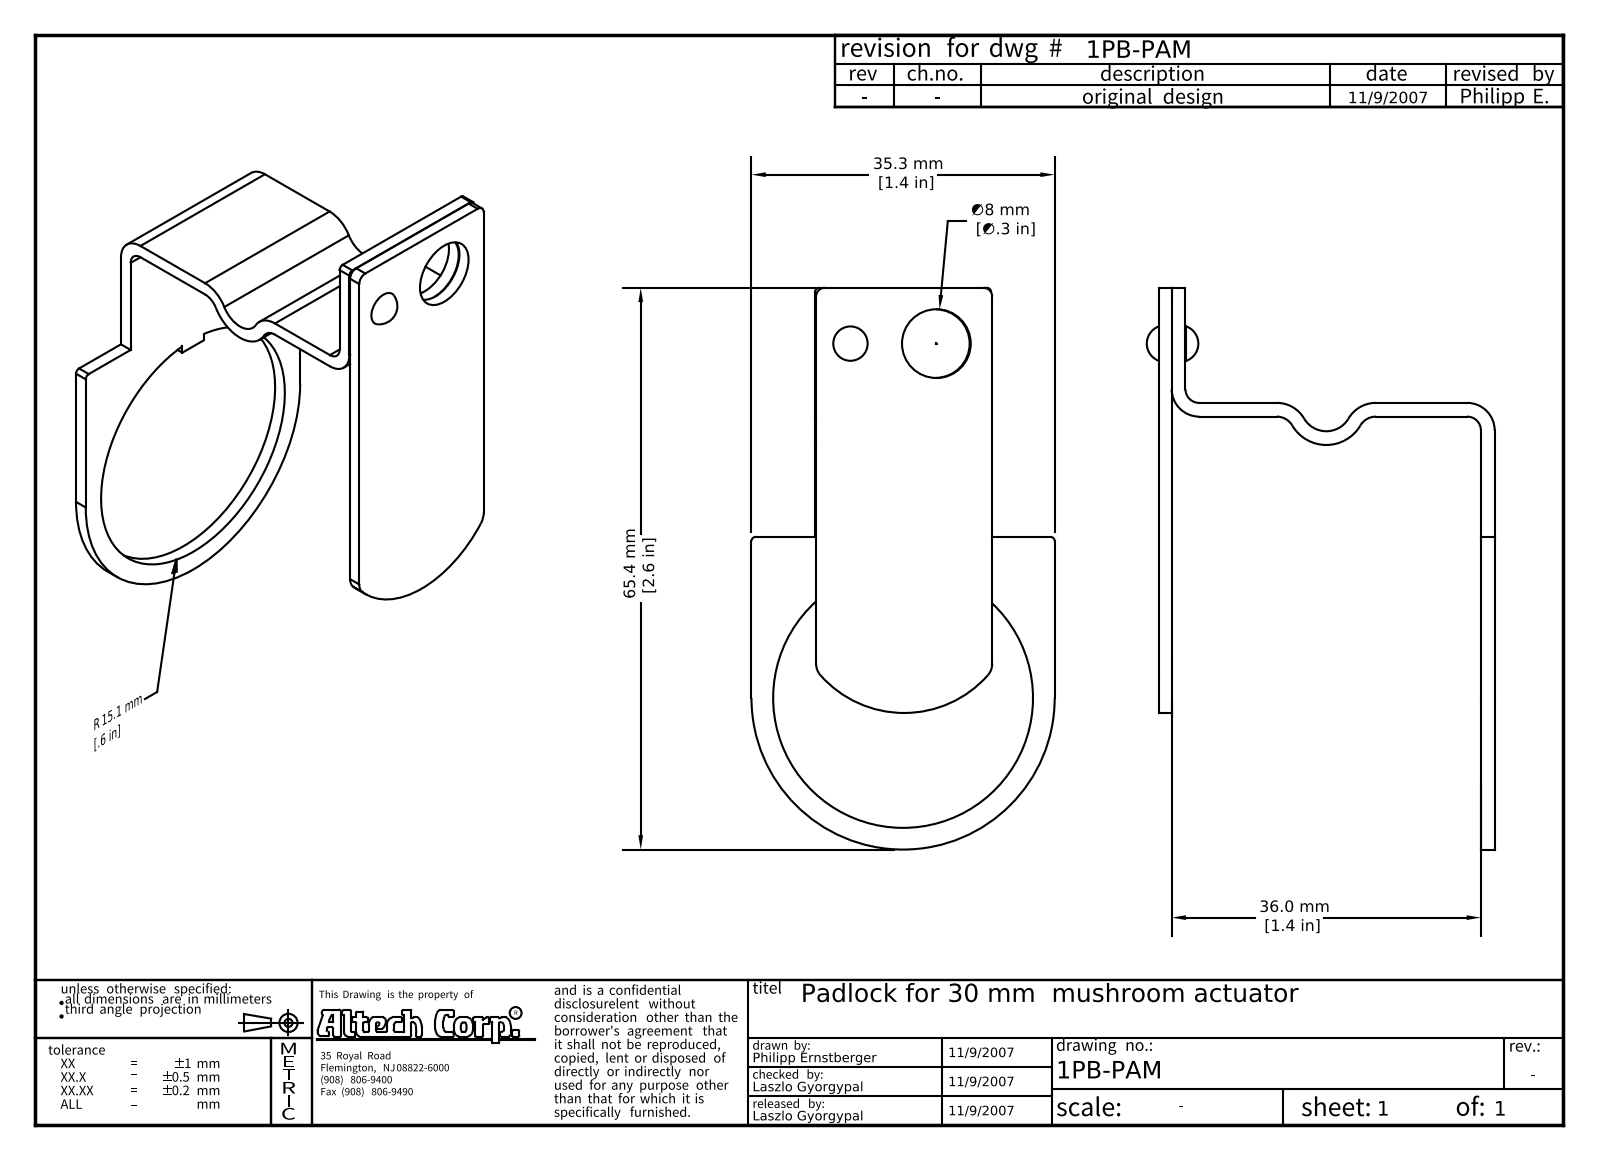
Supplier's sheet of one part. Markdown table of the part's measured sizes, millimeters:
| quantity | value |
| --- | --- |
| part name | PAM; standoff; top; SS 1440 - KN 2.3 x 18 x 3 |
| STEP written by | Autodesk Inventor 2008 (AUTOMOTIVE_DESIGN) |
| units | millimeters |
| bodies | 3 solids, 53 faces (25 planar, 26 cylindrical, 2 other) |
| overall size | 65.4 × 40.5 × 35.3 |
| volume | 4 177 mm³ |
| surface area | 6 241 mm² |
| round holes (diameter × count) | 8 × 2, 2.5 × 1, 30.25 × 1 |
| round bosses / shafts (diameter × count) | 2.3 × 1 |
| partial cylindrical surfaces (radius × count) | 0.5 × 4, 1 × 2, 1.6 × 2, 2 × 2, 2.06 × 2, 3.2 × 2, 3.66 × 2, 3 × 1 |
| main face-to-face distances | 1.6, 1.5, 36, 37.5, 37.6, 39.1, 34.4, 3.1, 20.5, 20.38 |
| hole center spacings | 9.88, 10, 41.42, 41.43, 41.7 |
